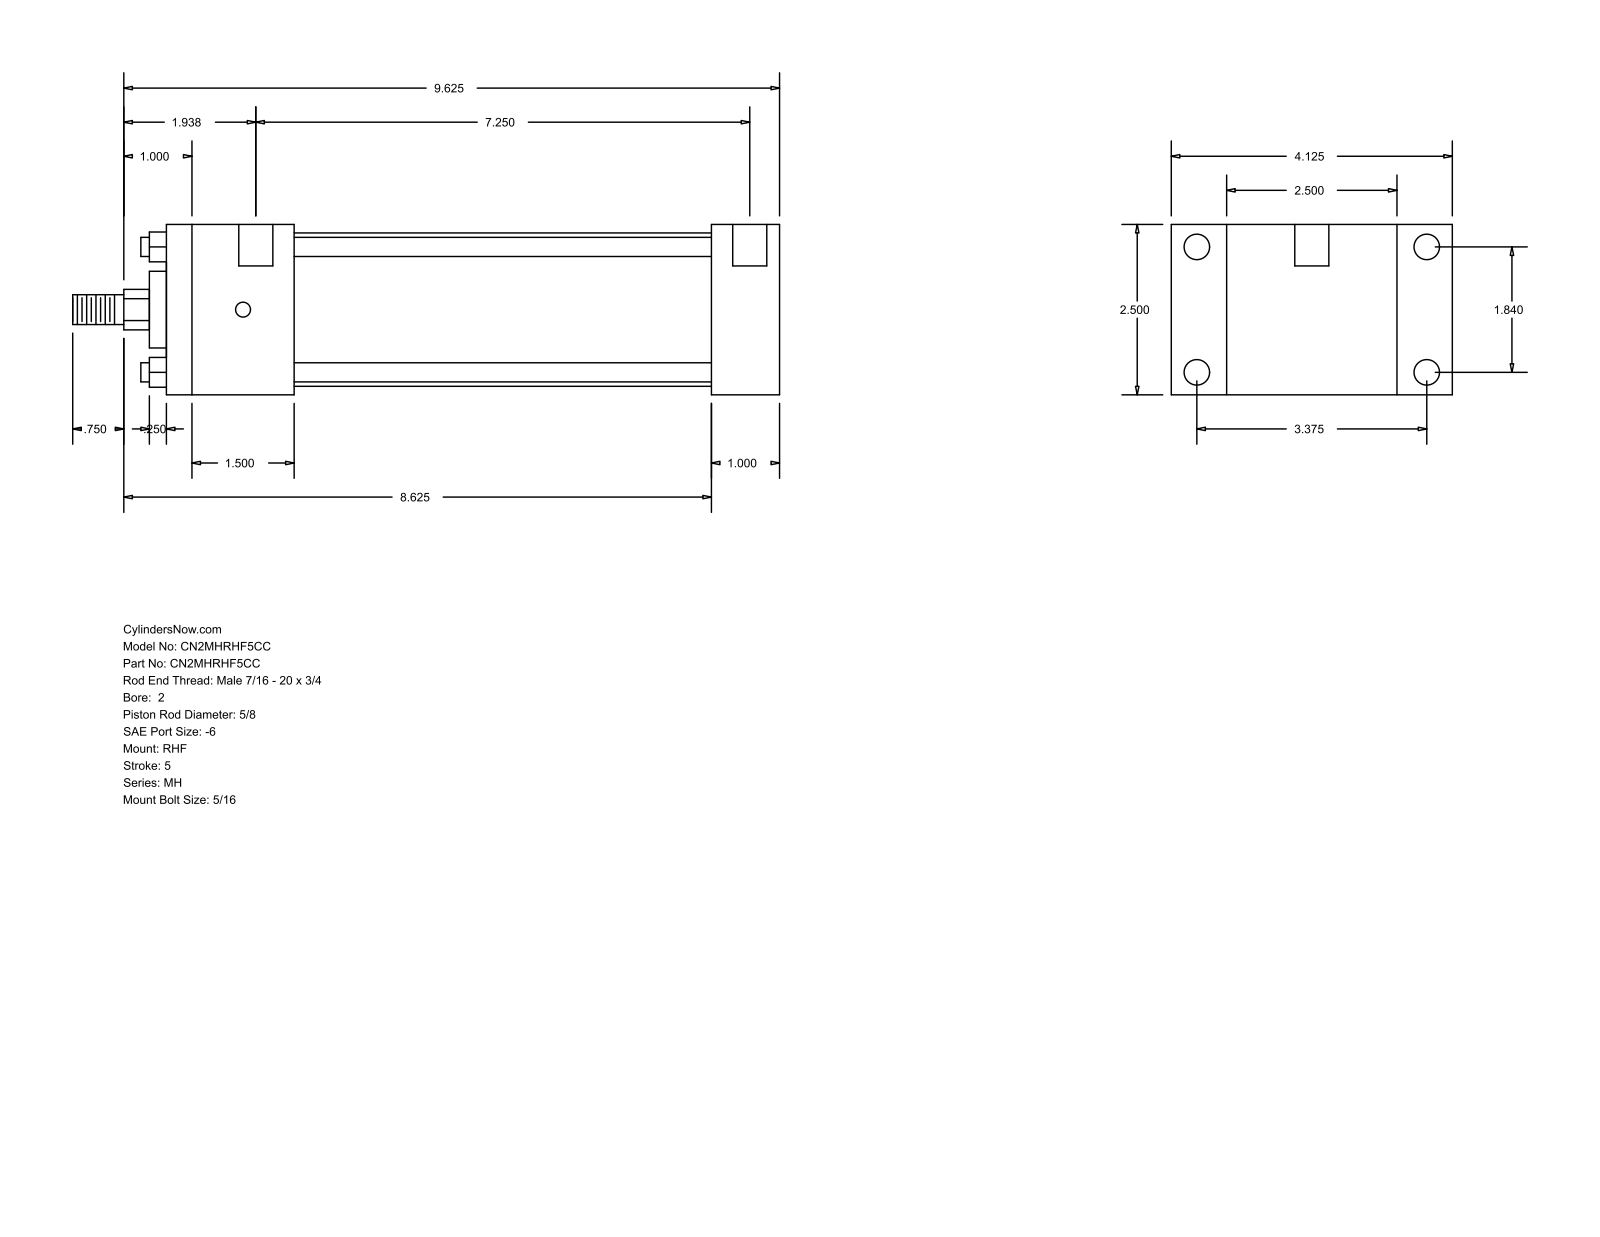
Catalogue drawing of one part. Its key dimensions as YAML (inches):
part_name: "MH_RHF__0200_0.625"
step_written_by: "GSSL Pune (CONFIG_CONTROL_DESIGN)"
units: inches
bodies: {solids: 0, faces: 88, planar: 60, cylindrical: 28, other: 0}
overall_size: [10.375, 4.125, 2.5]
round_holes:
  - {diameter: 0.219, count: 4}
  - {diameter: 0.375, count: 4}
  - {diameter: 0.5, count: 2}
round_bosses_or_shafts:
  - {diameter: 0.281, count: 4}
  - {diameter: 2.25, count: 1}
  - {diameter: 1.125, count: 1}
  - {diameter: 0.625, count: 1}
  - {diameter: 0.437, count: 1}
partial_cylinders:
  - {radius: 0.297, count: 1}
face_to_face_distances: [2.5, 1, 0.813, 3.313, 8, 9, 4.125, 1.875, 6.125, 7.125]
hole_center_spacings: [1.84, 3.375, 3.844, 7.563, 0.125, 0.187, 7.25, 7.375]
